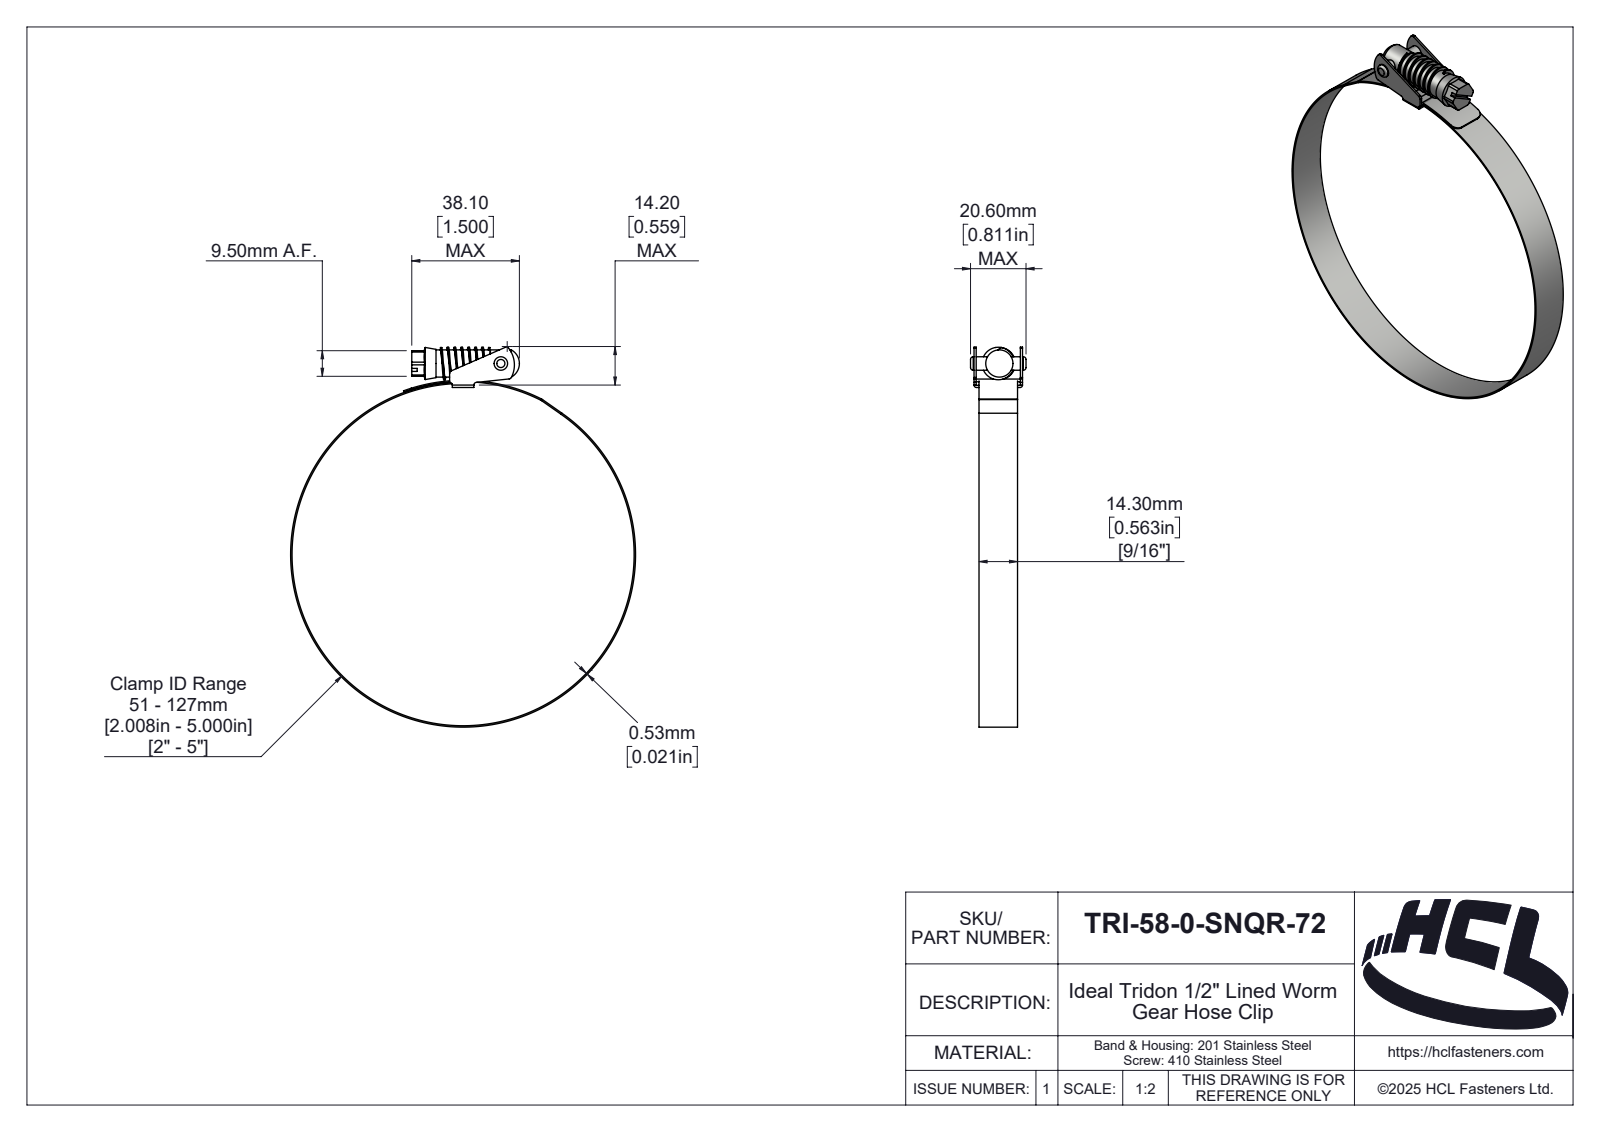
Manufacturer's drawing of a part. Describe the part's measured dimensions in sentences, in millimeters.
The part is named "TRI-58-0-SNQR-72". Its 3-D file was written by "SolidWorks 2025 (AUTOMOTIVE_DESIGN)". It is 5 solids with 222 faces: 44 planar, 112 cylindrical and 66 other. Overall it measures 141.02 by 128.06 by 20.6 millimeters. Its volume is 7 030 cubic millimeters and its surface area 16 508 square millimeters. Round holes: 1 of diameter 5, 1 of diameter 127. Round bosses or shafts: 1 of diameter 128.06, 1 of diameter 10.1. Partial cylindrical surfaces (rounded edges, fillets, slot ends): 11 of radius 1, 2 of radius 0.1, 2 of radius 0.9, 2 of radius 3, 1 of radius 0.46, 1 of radius 1.89, 1 of radius 2, 1 of radius 2.35. The main face-to-face distances are 0.8, 17.2, 1.85, 16.15, 1.05, 15.35, 14.3, 18, 16.4, 1. The hole center spacings are 72.27.
